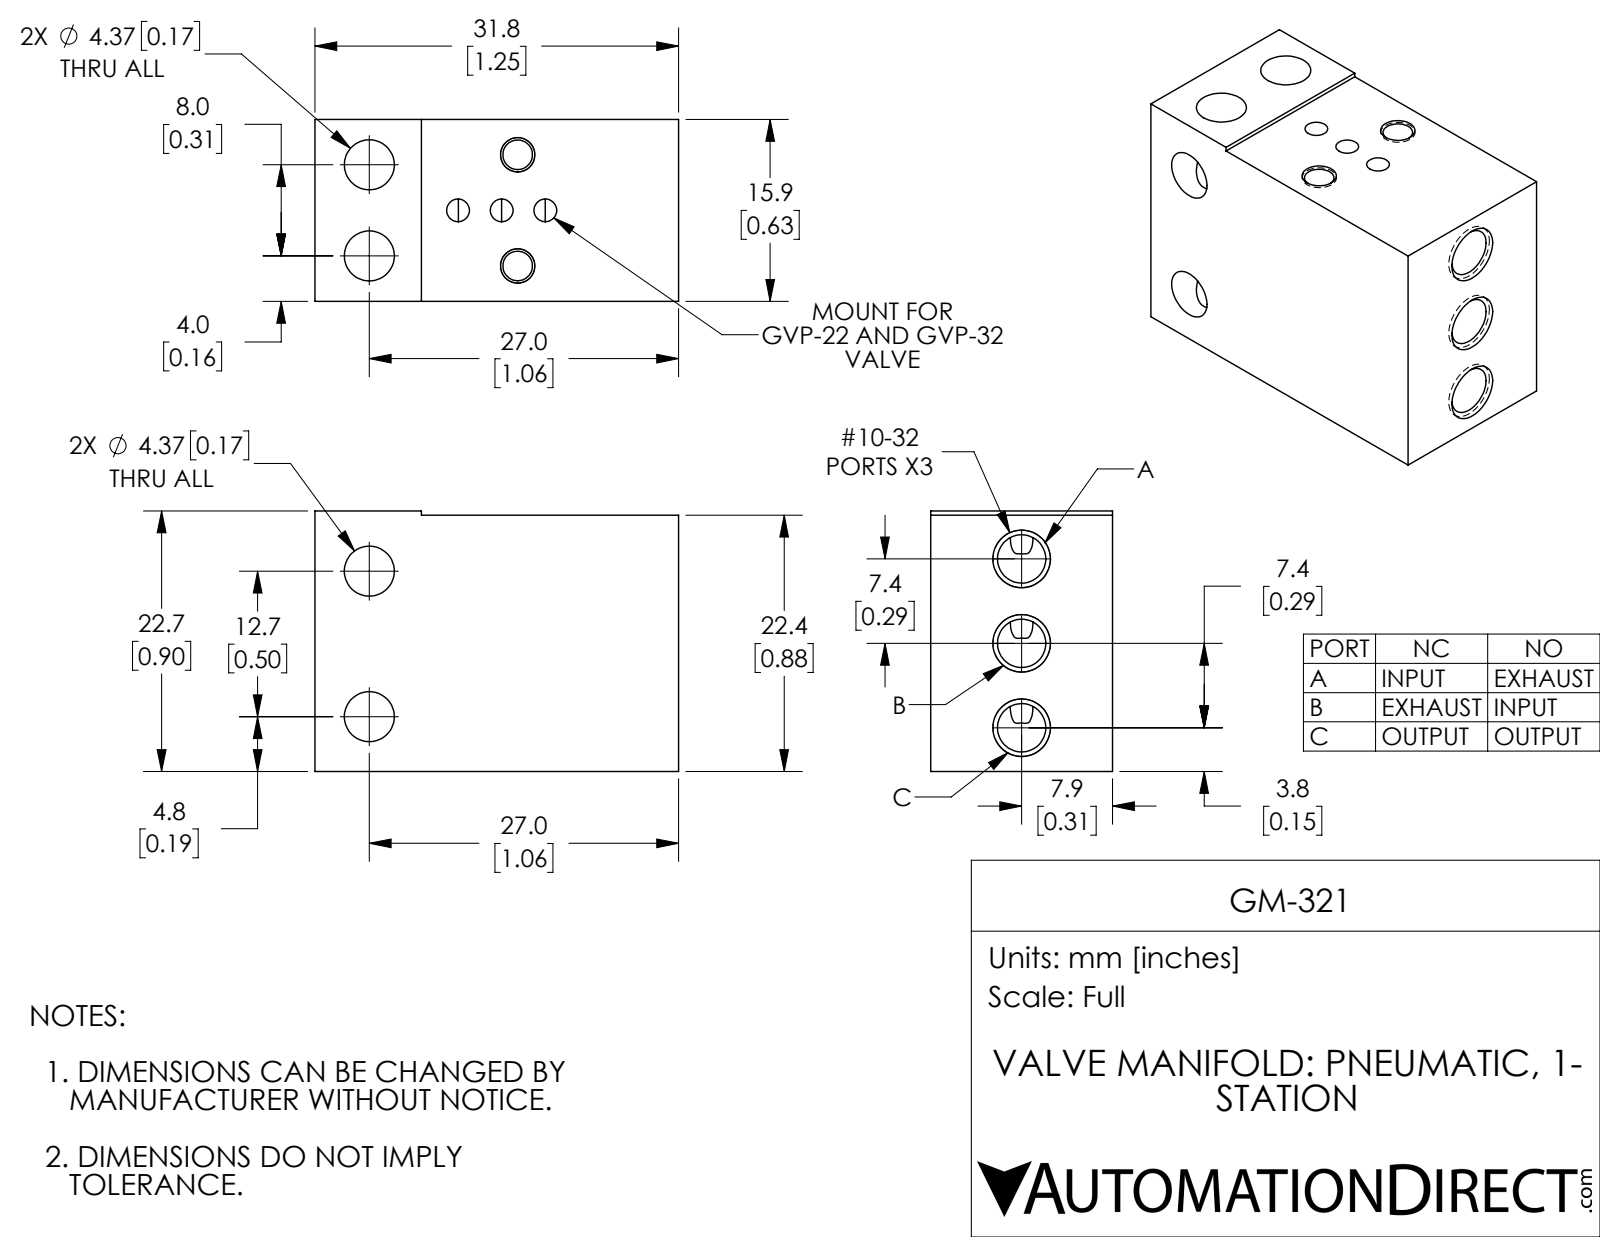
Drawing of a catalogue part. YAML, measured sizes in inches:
part_name: "GM-321"
step_written_by: "SolidWorks 2018 (AUTOMOTIVE_DESIGN)"
units: inches
bodies: {solids: 1, faces: 68, planar: 8, cylindrical: 40, other: 20}
overall_size: [1.25, 0.895, 0.625]
volume: 0.583
surface_area: 7.246
round_holes:
  - {diameter: 0.172, count: 4}
  - {diameter: 0.078, count: 3}
  - {diameter: 0.166, count: 3}
  - {diameter: 0.101, count: 2}
face_to_face_distances: [0.625, 0.88, 1.25, 0.895, 0.015, 0.366, 0.884]
hole_center_spacings: [0.15, 0.199, 0.213, 0.28, 0.343, 0.481, 0.511, 0.617]
